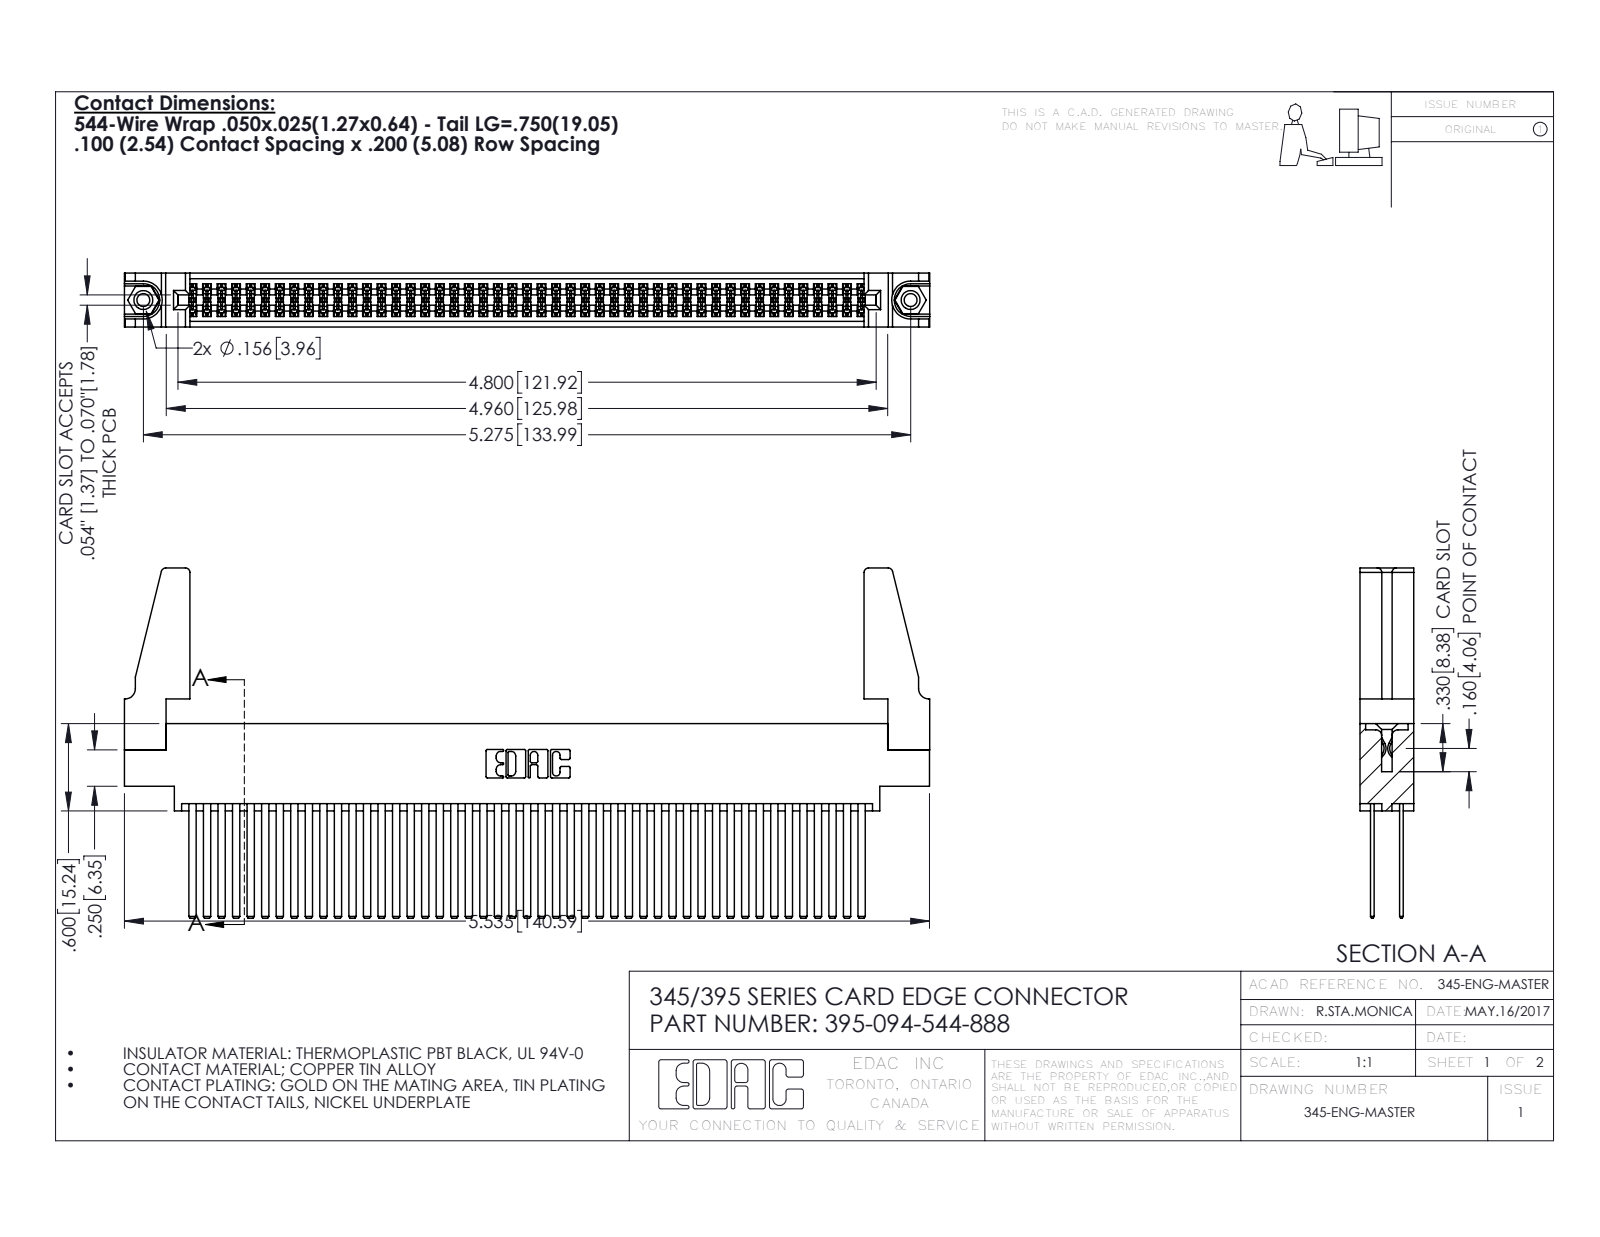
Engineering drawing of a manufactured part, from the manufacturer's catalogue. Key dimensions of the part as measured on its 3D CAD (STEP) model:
Part name (STEP PRODUCT): 345-292-001_345-293-144; 345-220-078_345-220-088; 395-094-544-888; 345-250-001_345-250-001-102 (+1 more)
STEP written by: SolidWorks 2016 (CONFIG_CONTROL_DESIGN)
Units: inches
Bodies: 99 solids, 4390 faces (2882 planar, 1492 cylindrical, 16 other)
Overall size (bounding box): 5.536 × 2.407 × 0.37
Volume: 1.108 in³ · Surface area: 45.36 in²
Round holes (diameter × count): ⌀0.089 ×2, ⌀0.125 ×2, ⌀0.156 ×2, ⌀0.064 ×1
Round bosses / shafts (diameter × count): ⌀0.155 ×2
Partial cylindrical surfaces — rounded edges, fillets, slot ends (radius × count): R0.006 ×141, R0.01 ×22, R0.03 ×8, R0.007 ×6, R0.031 ×6, R0.026 ×3, R0.014 ×2, R0.019 ×2
Main face-to-face distances: 0.072, 0.298, 0.2, 0.098, 0.272, 0.025, 0.225, 0.37, 0.175, 0.149
Hole centre spacings: 0.27, 5.039, 5.275
